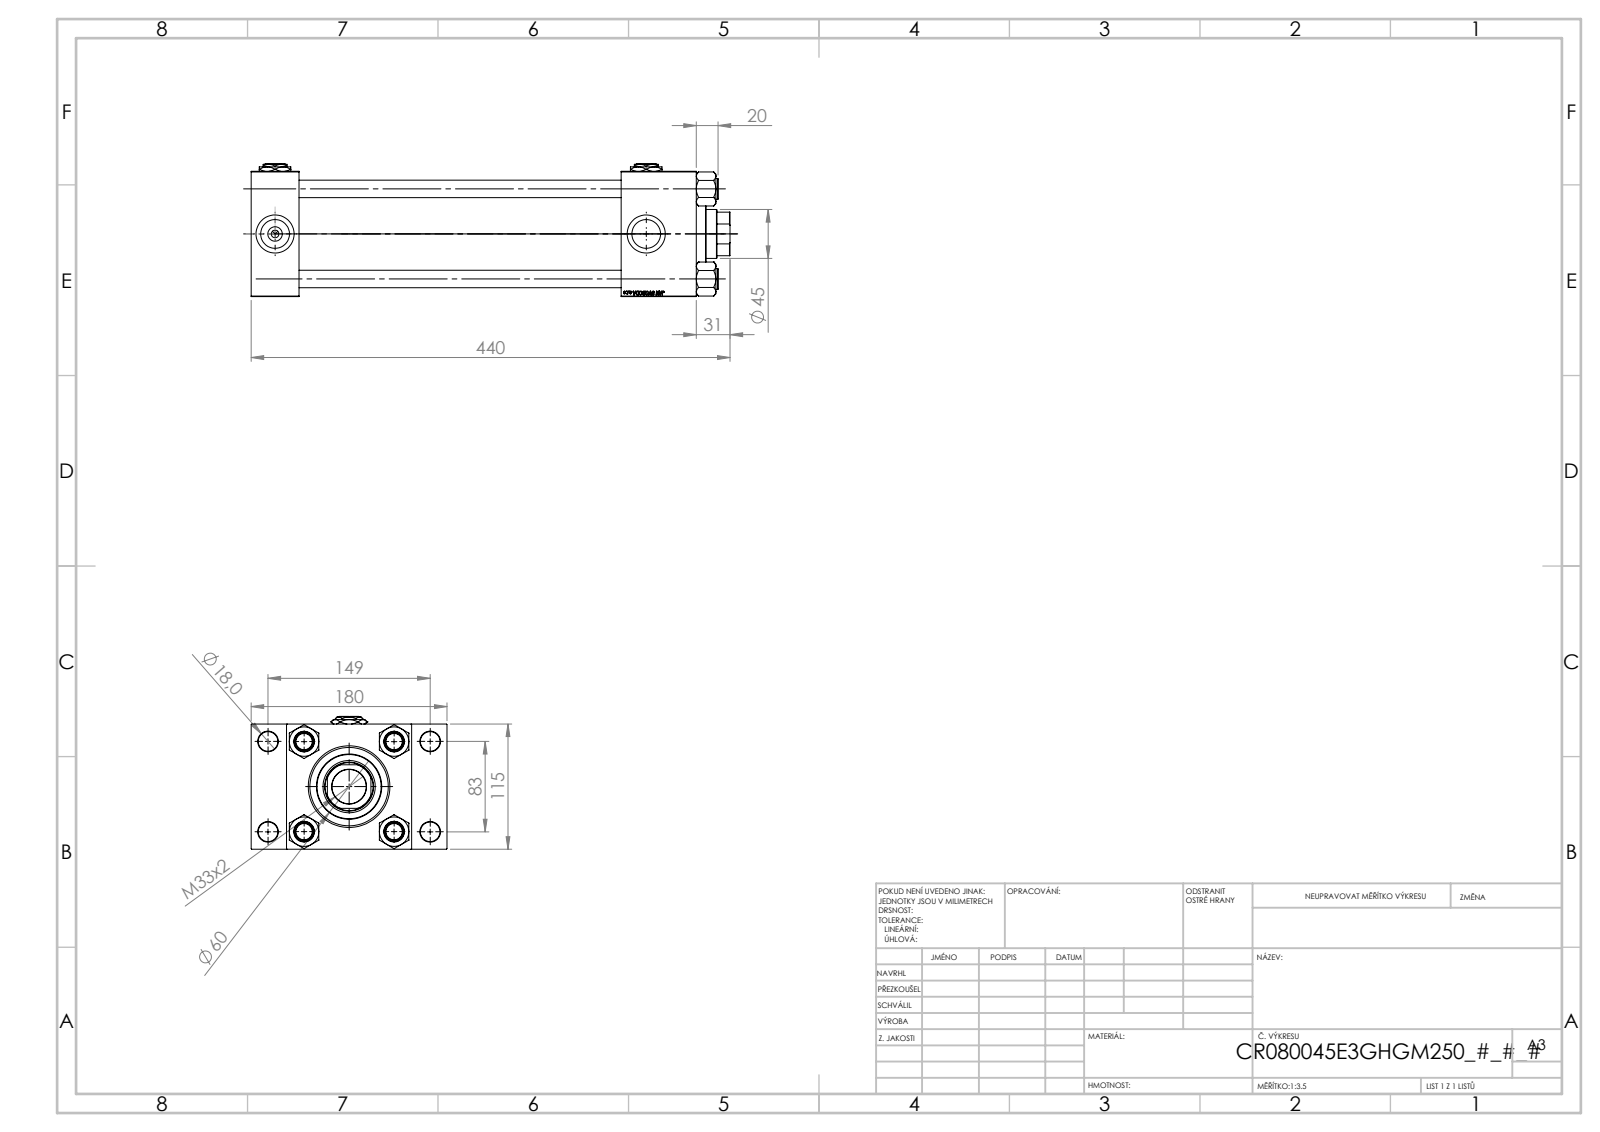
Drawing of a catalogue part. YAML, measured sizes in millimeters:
part_name: "NUT_M5_E; V215CR_E_Body; Zatka_pro_OIL_PORT; V215CR_VCP_E (+2 more)"
step_written_by: "SolidWorks 2019 (CONFIG_CONTROL_DESIGN)"
units: millimeters
bodies: {solids: 13, faces: 1290, planar: 595, cylindrical: 101, other: 594}
overall_size: [440, 180, 122]
volume: 2833000
surface_area: 521530
round_holes:
  - {diameter: 16, count: 4}
  - {diameter: 18, count: 4}
  - {diameter: 26.44, count: 4}
  - {diameter: 35, count: 4}
  - {diameter: 7, count: 3}
  - {diameter: 2.5, count: 2}
  - {diameter: 31.5, count: 1}
  - {diameter: 45, count: 1}
  - {diameter: 48, count: 1}
  - {diameter: 61, count: 1}
  - {diameter: 72, count: 1}
  - {diameter: 80, count: 1}
round_bosses_or_shafts:
  - {diameter: 19, count: 4}
  - {diameter: 86, count: 1}
  - {diameter: 60, count: 1}
partial_cylinders:
  - {radius: 22, count: 1}
face_to_face_distances: [115, 44, 409, 365, 32.5, 147.5, 69, 340, 296, 180]
hole_center_spacings: [33.15, 41.96, 57.81, 58.48, 82.7, 85.28, 86.17, 89.24]
